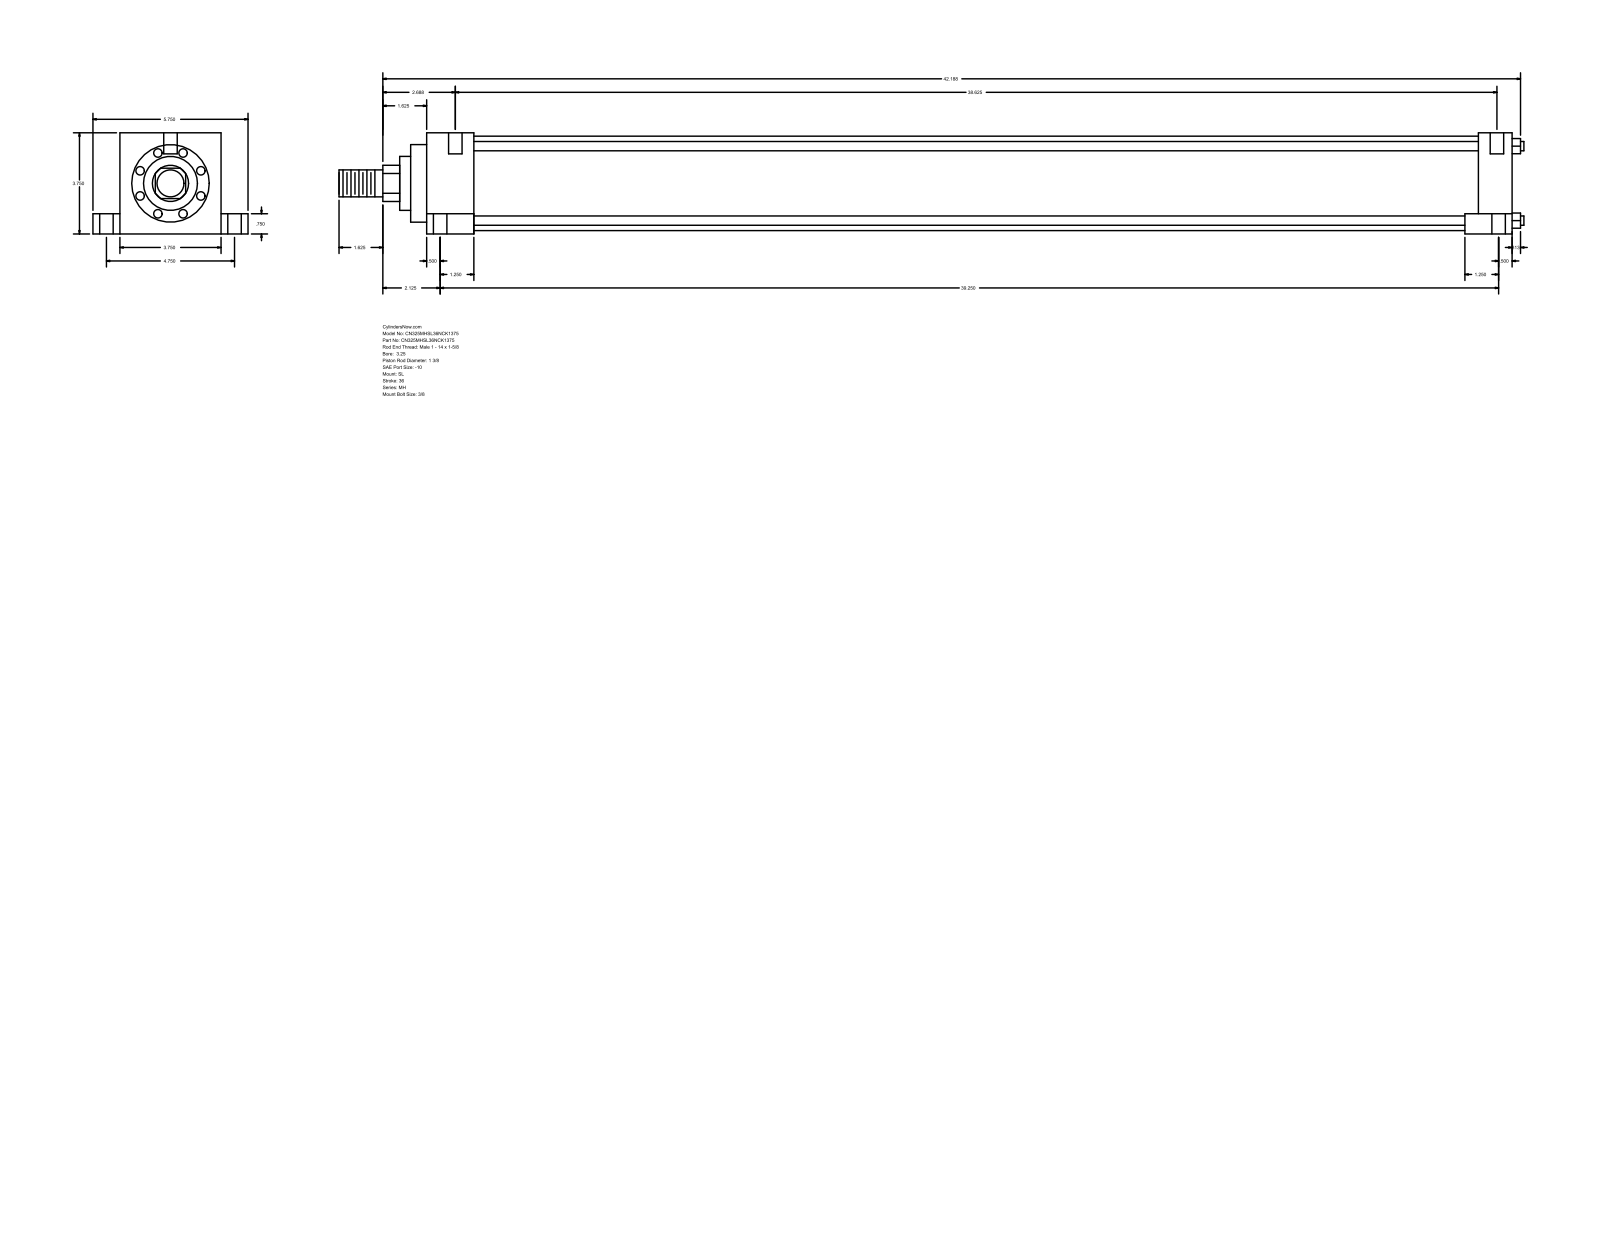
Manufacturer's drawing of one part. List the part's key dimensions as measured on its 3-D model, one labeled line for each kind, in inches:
Part name (STEP PRODUCT): MH_SL__0325_1.375
STEP written by: GSSL Pune (CONFIG_CONTROL_DESIGN)
Units: inches
Bodies: 0 solids, 110 faces (77 planar, 33 cylindrical, 0 other)
Overall size (bounding box): 43.937 × 5.75 × 3.75
Round holes (diameter × count): ⌀0.5 ×6, ⌀0.219 ×4, ⌀0.75 ×4
Round bosses / shafts (diameter × count): ⌀0.345 ×4, ⌀3.5 ×1, ⌀2.875 ×1, ⌀2 ×1, ⌀1.375 ×1, ⌀1 ×1
Partial cylindrical surfaces — rounded edges, fillets, slot ends (radius × count): R0.672 ×1
Main face-to-face distances: 3.75, 40.25, 1.75, 38.5, 1, 4.75, 0.75, 3, 39, 37.25
Hole centre spacings: 2.376, 2.378, 2.427, 2.441, 4.75, 38.76, 38.823, 38.875
